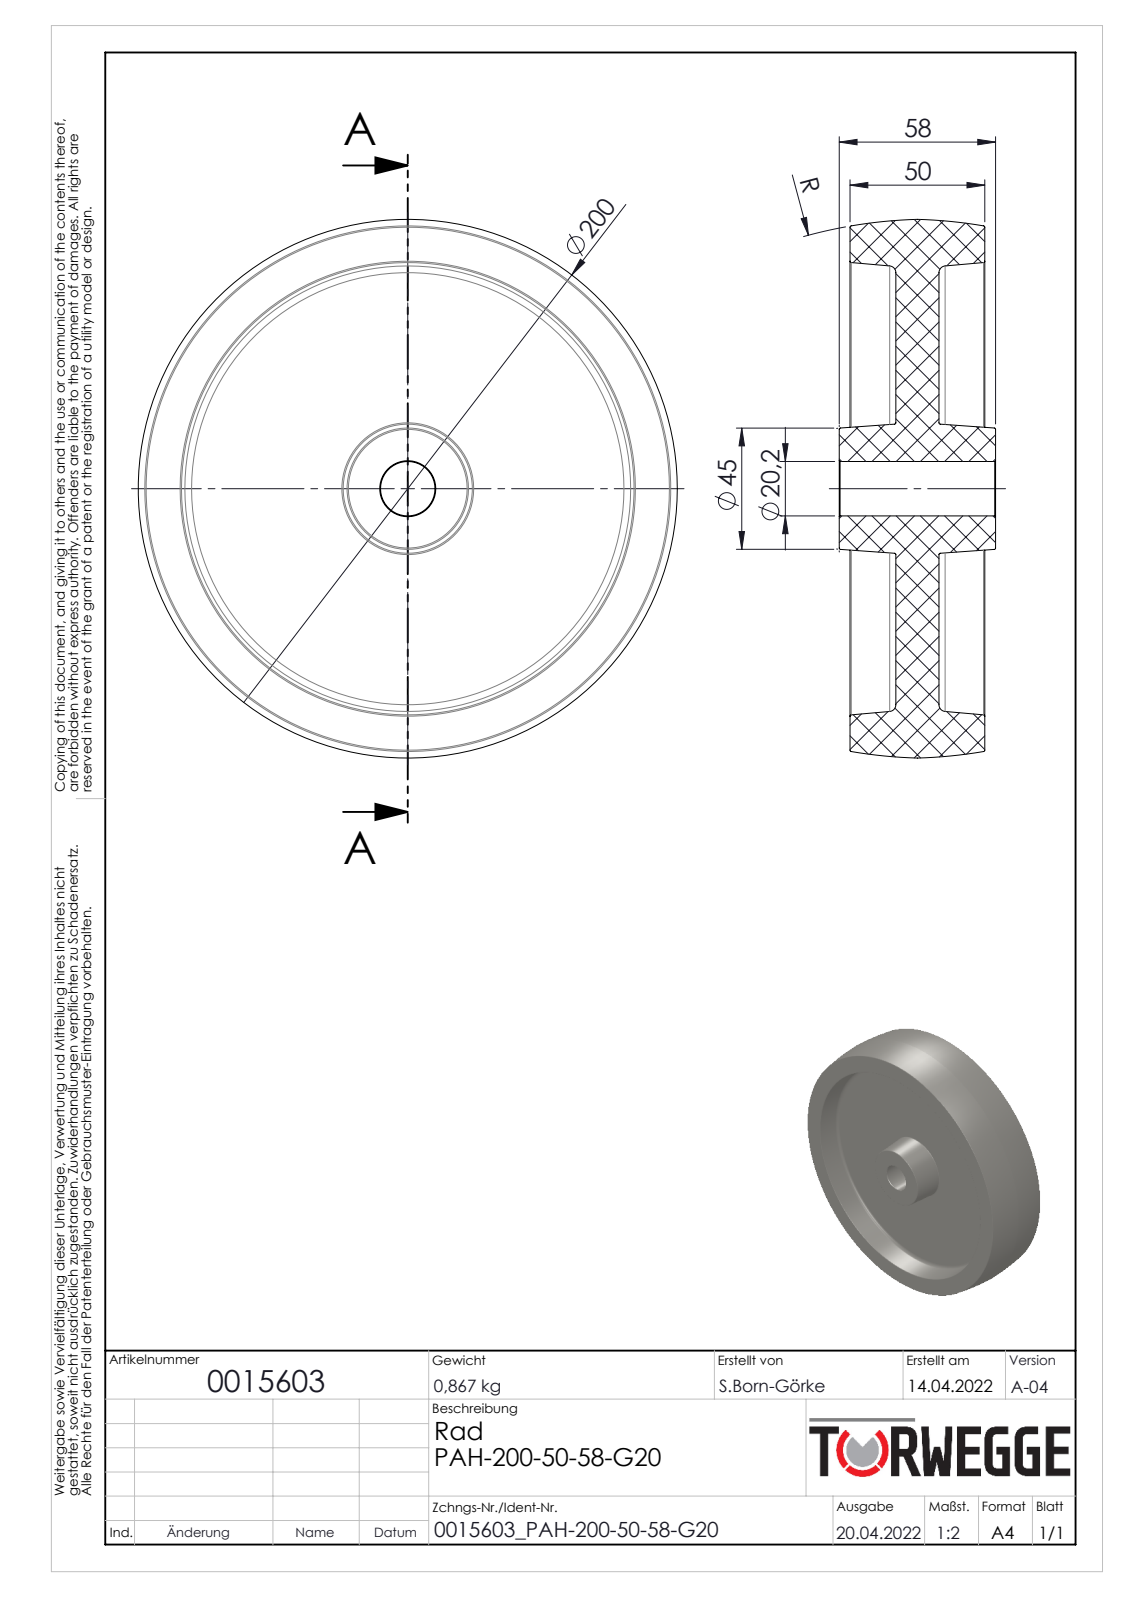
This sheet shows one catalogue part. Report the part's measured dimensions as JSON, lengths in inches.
{"part_name": "0015603", "step_written_by": "SolidWorks 2020 (AUTOMOTIVE_DESIGN)", "units": "inches", "bodies": {"solids": 1, "faces": 44, "planar": 6, "cylindrical": 2, "other": 36}, "overall_size": [7.874, 7.874, 2.283], "volume_in3": 52.16, "surface_area_in2": 177.7, "round_holes": [[0.795, 1]], "face_to_face_distances": [0.63, 0.669, 1.299, 1.969, 0.157, 0.827, 1.457, 2.126, 2.283]}
